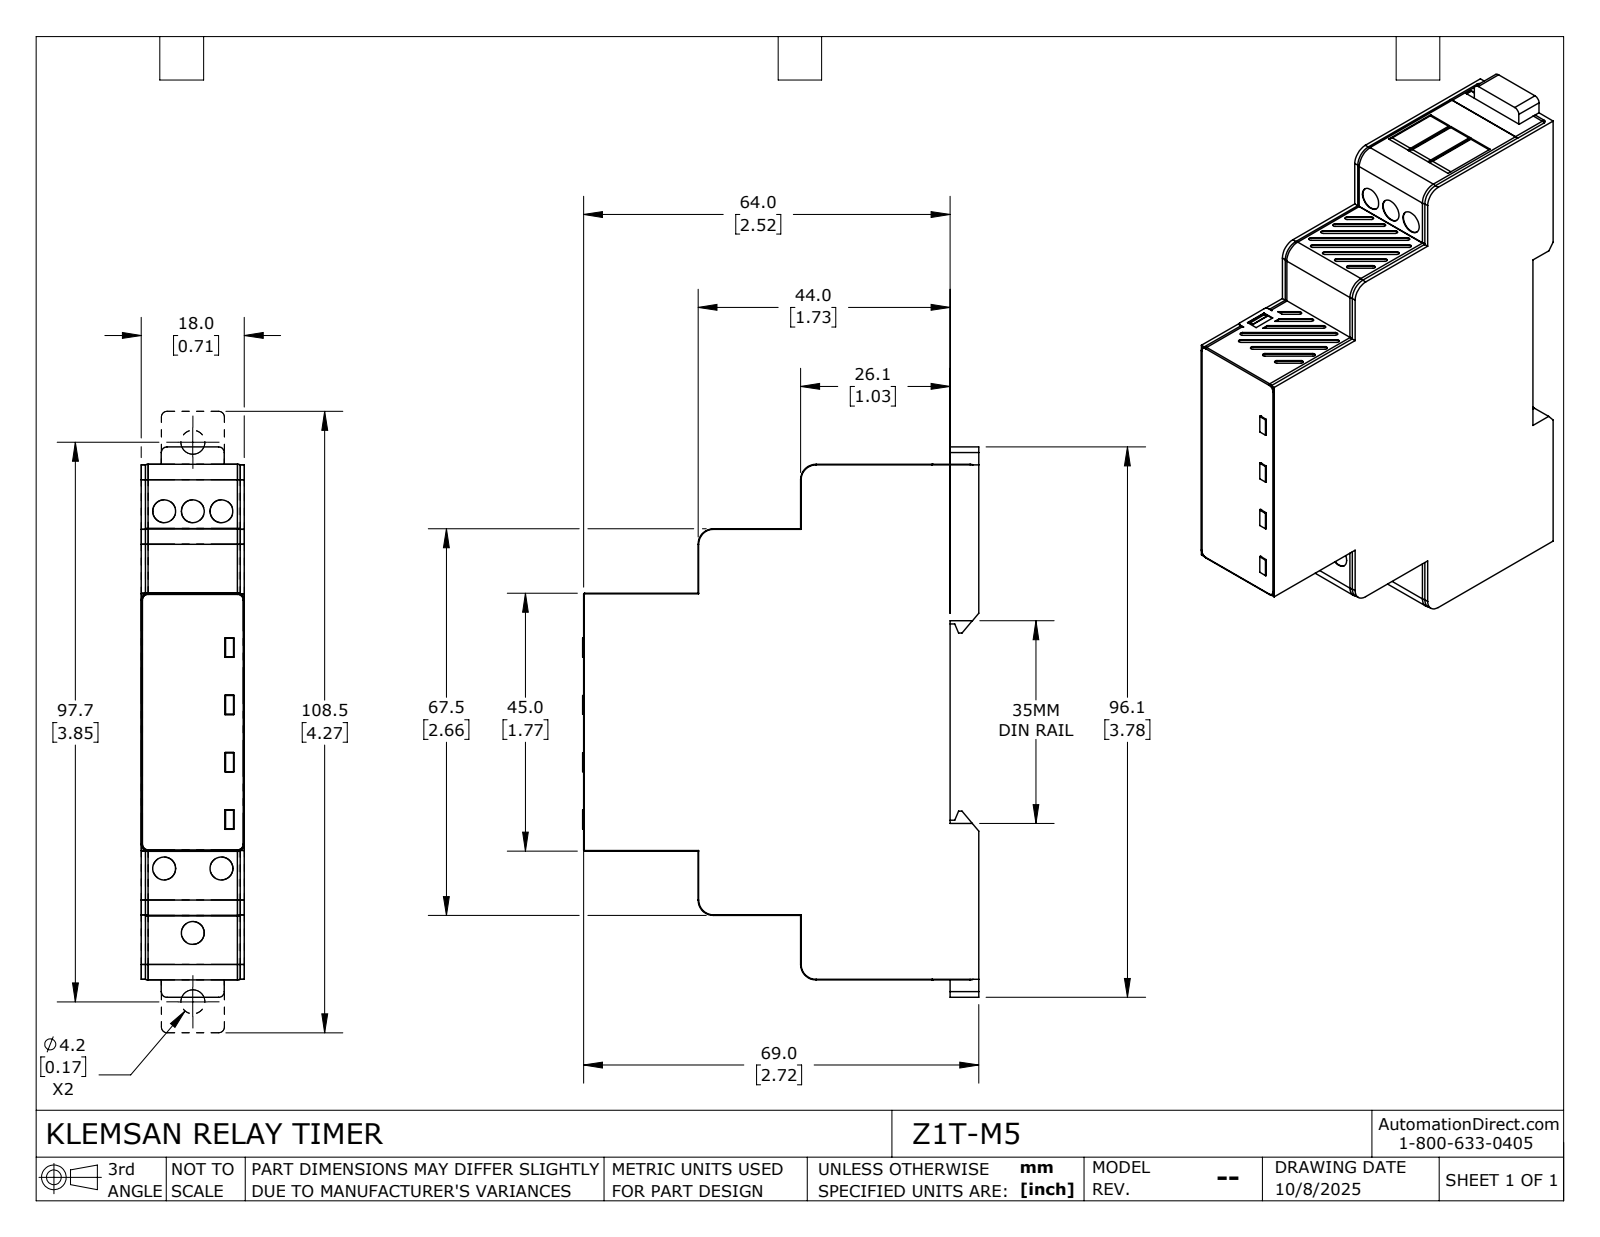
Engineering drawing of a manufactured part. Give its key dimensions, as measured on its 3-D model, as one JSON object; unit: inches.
{"part_name": "Z1T-M5", "step_written_by": "SolidWorks 2024 (CONFIG_CONTROL_DESIGN)", "units": "inches", "bodies": {"solids": 3, "faces": 440, "planar": 280, "cylindrical": 60, "other": 100}, "overall_size": [3.782, 2.722, 0.709], "volume_in3": 5.117, "surface_area_in2": 27.72, "round_holes": [[0.165, 2], [0.157, 1]], "partial_cylinders_radius": [[0.047, 16], [0.008, 4], [0.039, 4], [0.102, 4], [0.106, 4], [0.02, 2], [0.059, 2]], "face_to_face_distances": [0.709, 0.138, 0.571, 0.443, 2.52, 0.197, 2.717, 0.886, 2.654, 2.657], "hole_center_spacings": [0.23, 3.127, 3.357]}
